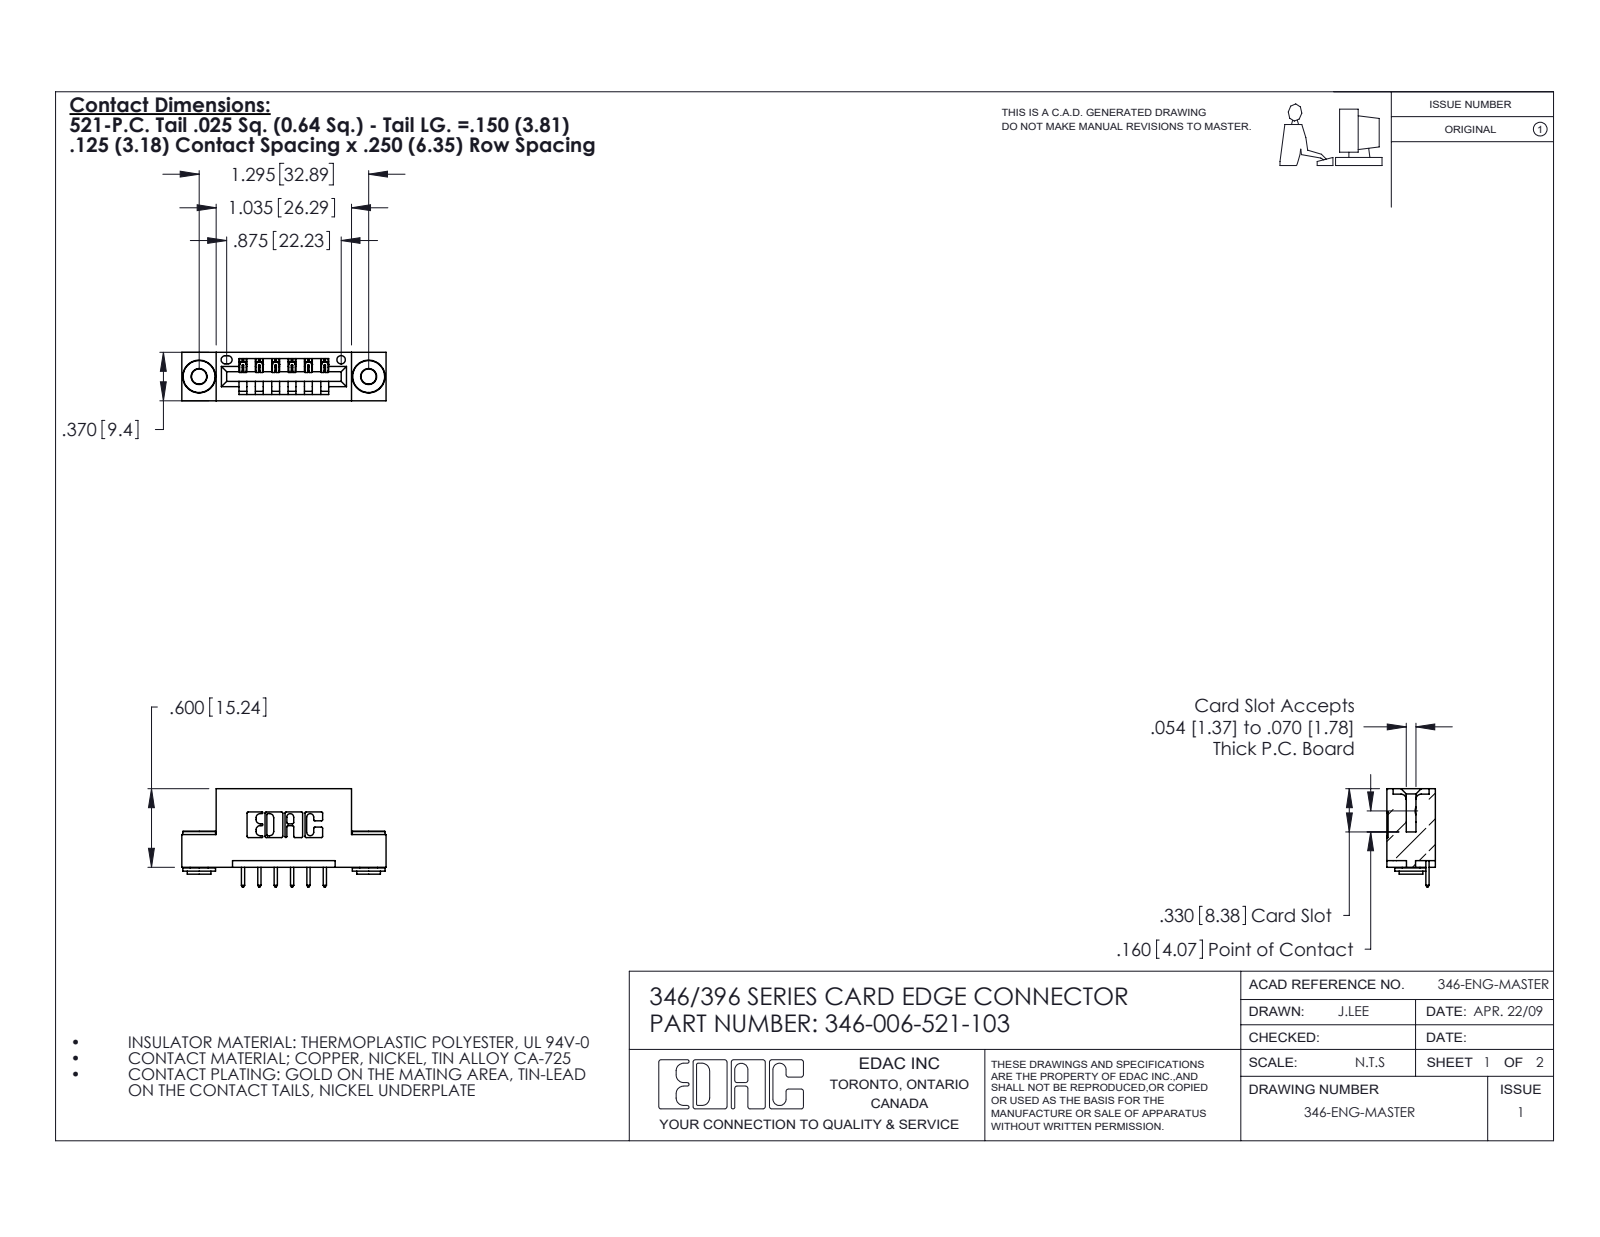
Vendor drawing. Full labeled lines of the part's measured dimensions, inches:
Part name (STEP PRODUCT): 345-292-001_345-293-121; 346 Part_Flush Mounting Lugs - 0.156 Dia-TH; 345-250-002_345-250-002-102; 346-006-521-103
STEP written by: SolidWorks 2020 (CONFIG_CONTROL_DESIGN)
Units: inches
Bodies: 9 solids, 522 faces (340 planar, 174 cylindrical, 8 other)
Overall size (bounding box): 1.56 × 0.75 × 0.37
Volume: 0.215 in³ · Surface area: 6.519 in²
Round holes (diameter × count): ⌀0.116 ×2, ⌀0.156 ×2, ⌀0.064 ×1
Round bosses / shafts (diameter × count): ⌀0.25 ×2, ⌀0.18 ×2, ⌀0.136 ×2
Partial cylindrical surfaces — rounded edges, fillets, slot ends (radius × count): R0.01 ×22, R0.006 ×12, R0.01 ×12, R0.007 ×6, R0.031 ×6, R0.026 ×3, R0.031 ×2, R0.04 ×2
Main face-to-face distances: 0.25, 0.37, 0.048, 0.322, 0.025, 0.148, 0.222, 0.1, 0.174, 0.125
Hole centre spacings: 0.246, 1.092, 1.295
